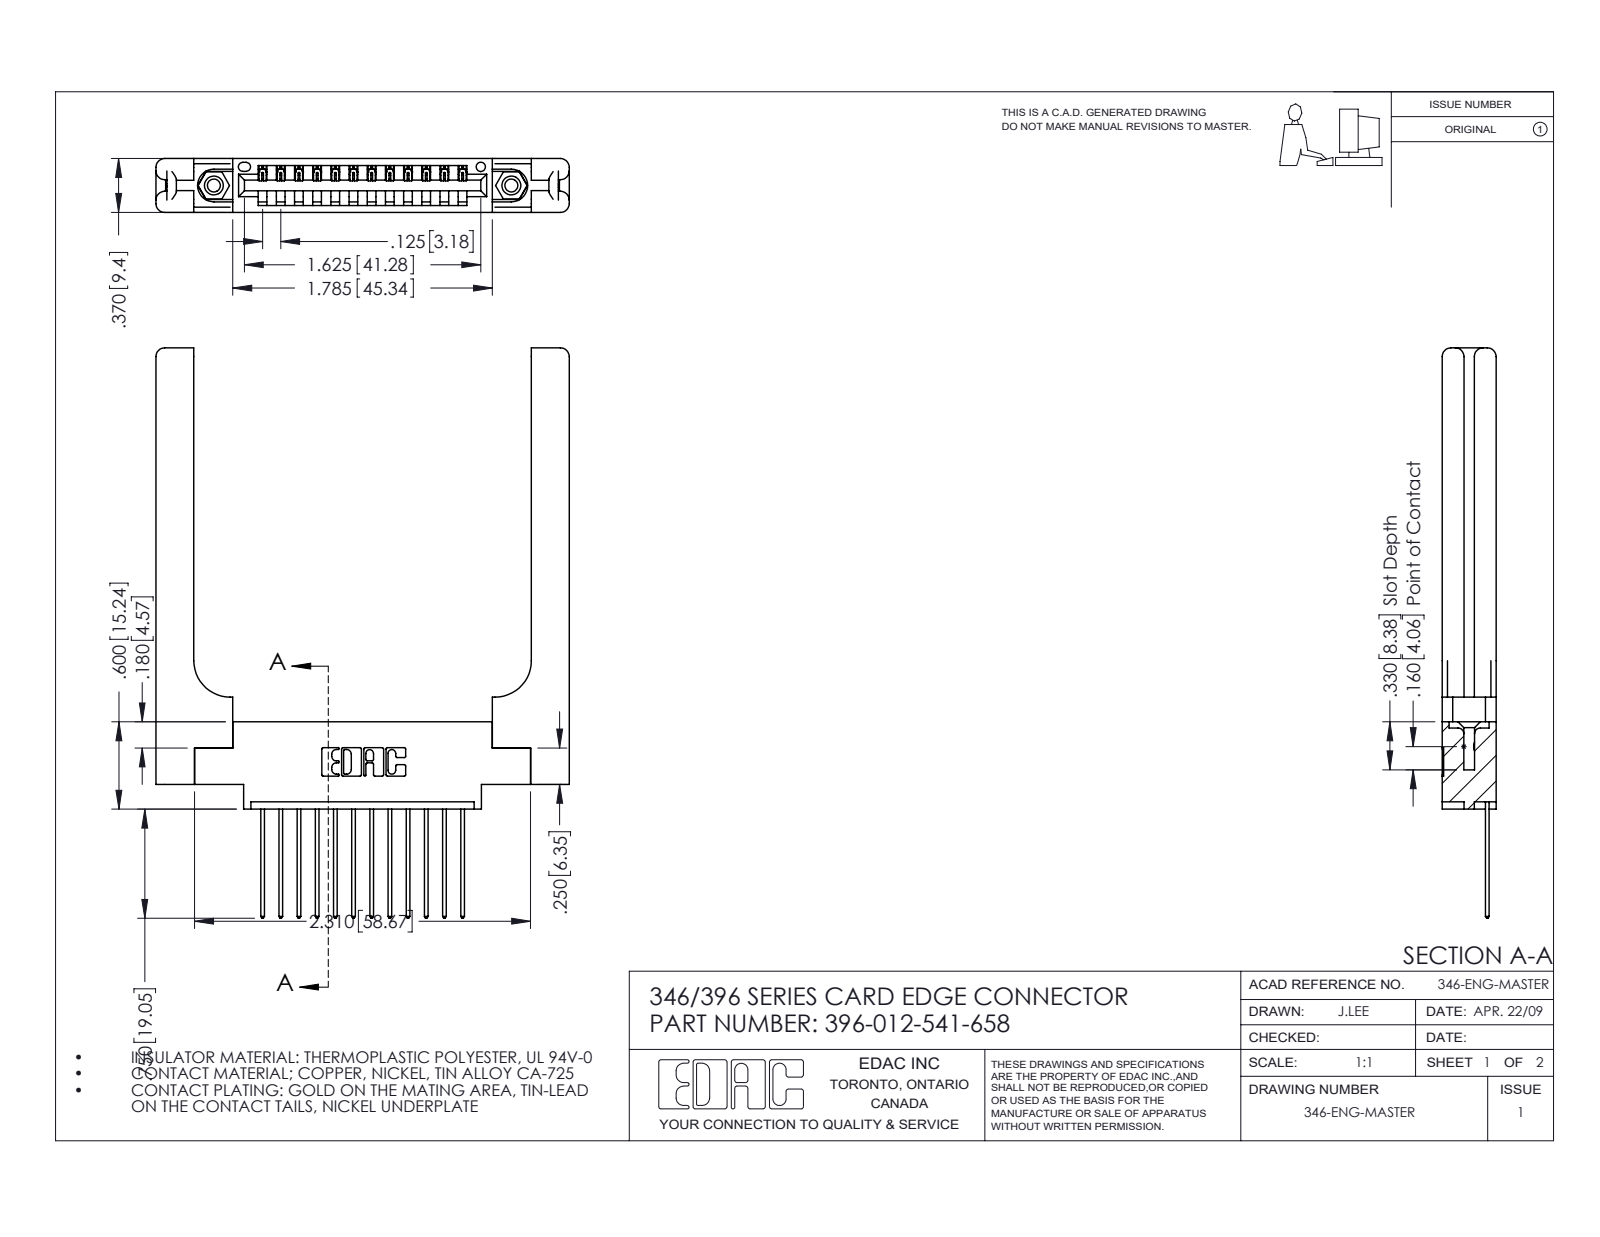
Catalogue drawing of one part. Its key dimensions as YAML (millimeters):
part_name: "396-012-541-658; 346-220-058_345-220-058; 345-292-001_345-293-141; 345-250-001_345-250-001-102 (+1 more)"
step_written_by: "SolidWorks 2016 (CONFIG_CONTROL_DESIGN)"
units: millimeters
bodies: {solids: 17, faces: 1078, planar: 708, cylindrical: 310, other: 60}
overall_size: [99.6, 72.2, 9.4]
volume: 14100
surface_area: 13470
round_holes:
  - {diameter: 2.3, count: 2}
  - {diameter: 3.2, count: 2}
  - {diameter: 4, count: 2}
  - {diameter: 1.6, count: 1}
round_bosses_or_shafts:
  - {diameter: 3.9, count: 2}
partial_cylinders:
  - {radius: 0.2, count: 24}
  - {radius: 0.3, count: 24}
  - {radius: 0.3, count: 22}
  - {radius: 1.5, count: 16}
  - {radius: 0.2, count: 6}
  - {radius: 0.8, count: 6}
  - {radius: 0.7, count: 3}
  - {radius: 0.8, count: 2}
face_to_face_distances: [9.4, 3.8, 1.8, 3.8, 1.2, 8.2, 5.6, 6.4, 2.6, 4.4]
hole_center_spacings: [6.2, 46.7, 51.9]
